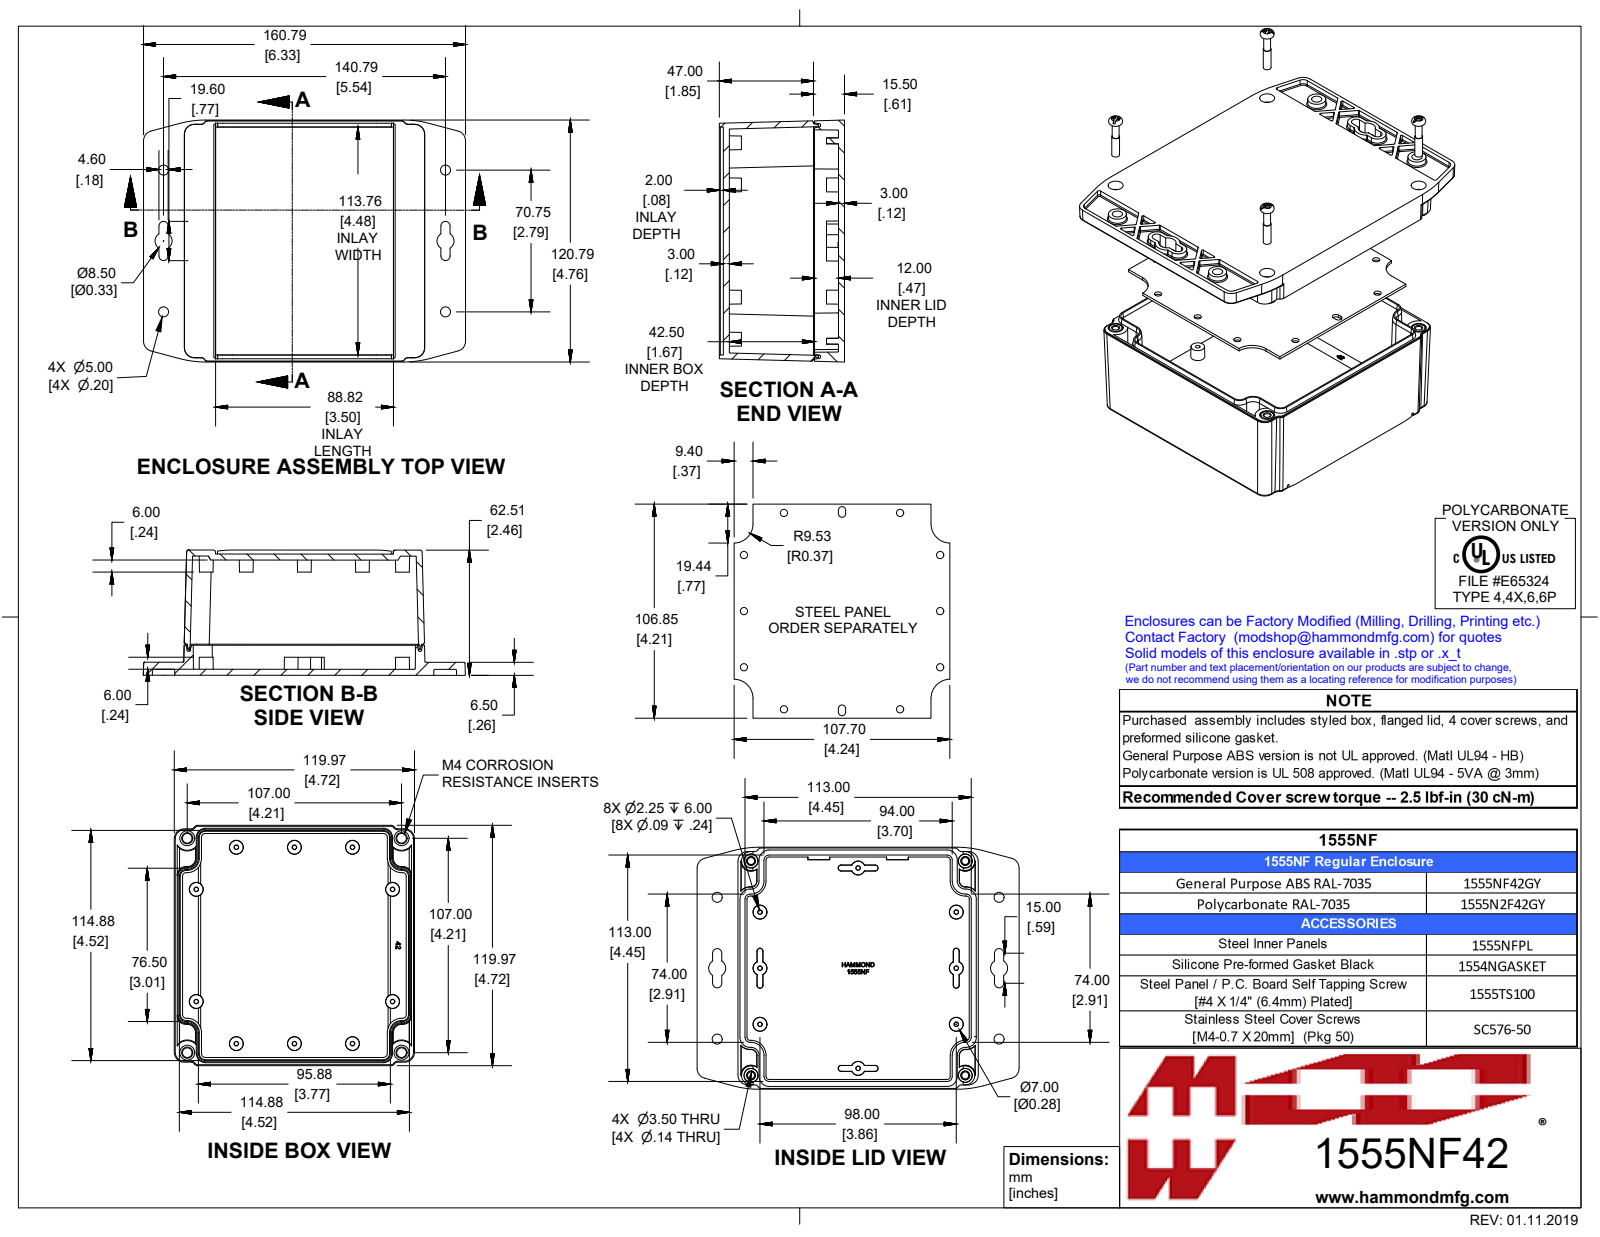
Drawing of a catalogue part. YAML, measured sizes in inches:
part_name: "1555NF42GY"
step_written_by: "SolidWorks 2019 (CONFIG_CONTROL_DESIGN)"
units: inches
bodies: {solids: 10, faces: 1338, planar: 603, cylindrical: 271, other: 464}
overall_size: [6.33, 4.755, 2.461]
volume: 12.88
surface_area: 224.6
round_holes:
  - {diameter: 0.128, count: 4}
  - {diameter: 0.138, count: 4}
  - {diameter: 0.295, count: 4}
round_bosses_or_shafts:
  - {diameter: 0.354, count: 4}
  - {diameter: 0.25, count: 4}
  - {diameter: 0.218, count: 4}
  - {diameter: 0.21, count: 4}
  - {diameter: 0.153, count: 4}
  - {diameter: 0.135, count: 4}
partial_cylinders:
  - {radius: 0.02, count: 132}
  - {radius: 0.197, count: 12}
  - {radius: 0.039, count: 10}
  - {radius: 0.089, count: 4}
  - {radius: 0.138, count: 4}
  - {radius: 0.169, count: 4}
  - {radius: 0.187, count: 4}
  - {radius: 0.246, count: 2}
face_to_face_distances: [0.118, 2.264, 2.146, 2.382, 0.079, 0.256, 0.059, 2.343, 0.138, 2.008]
hole_center_spacings: [4.213, 5.957]
